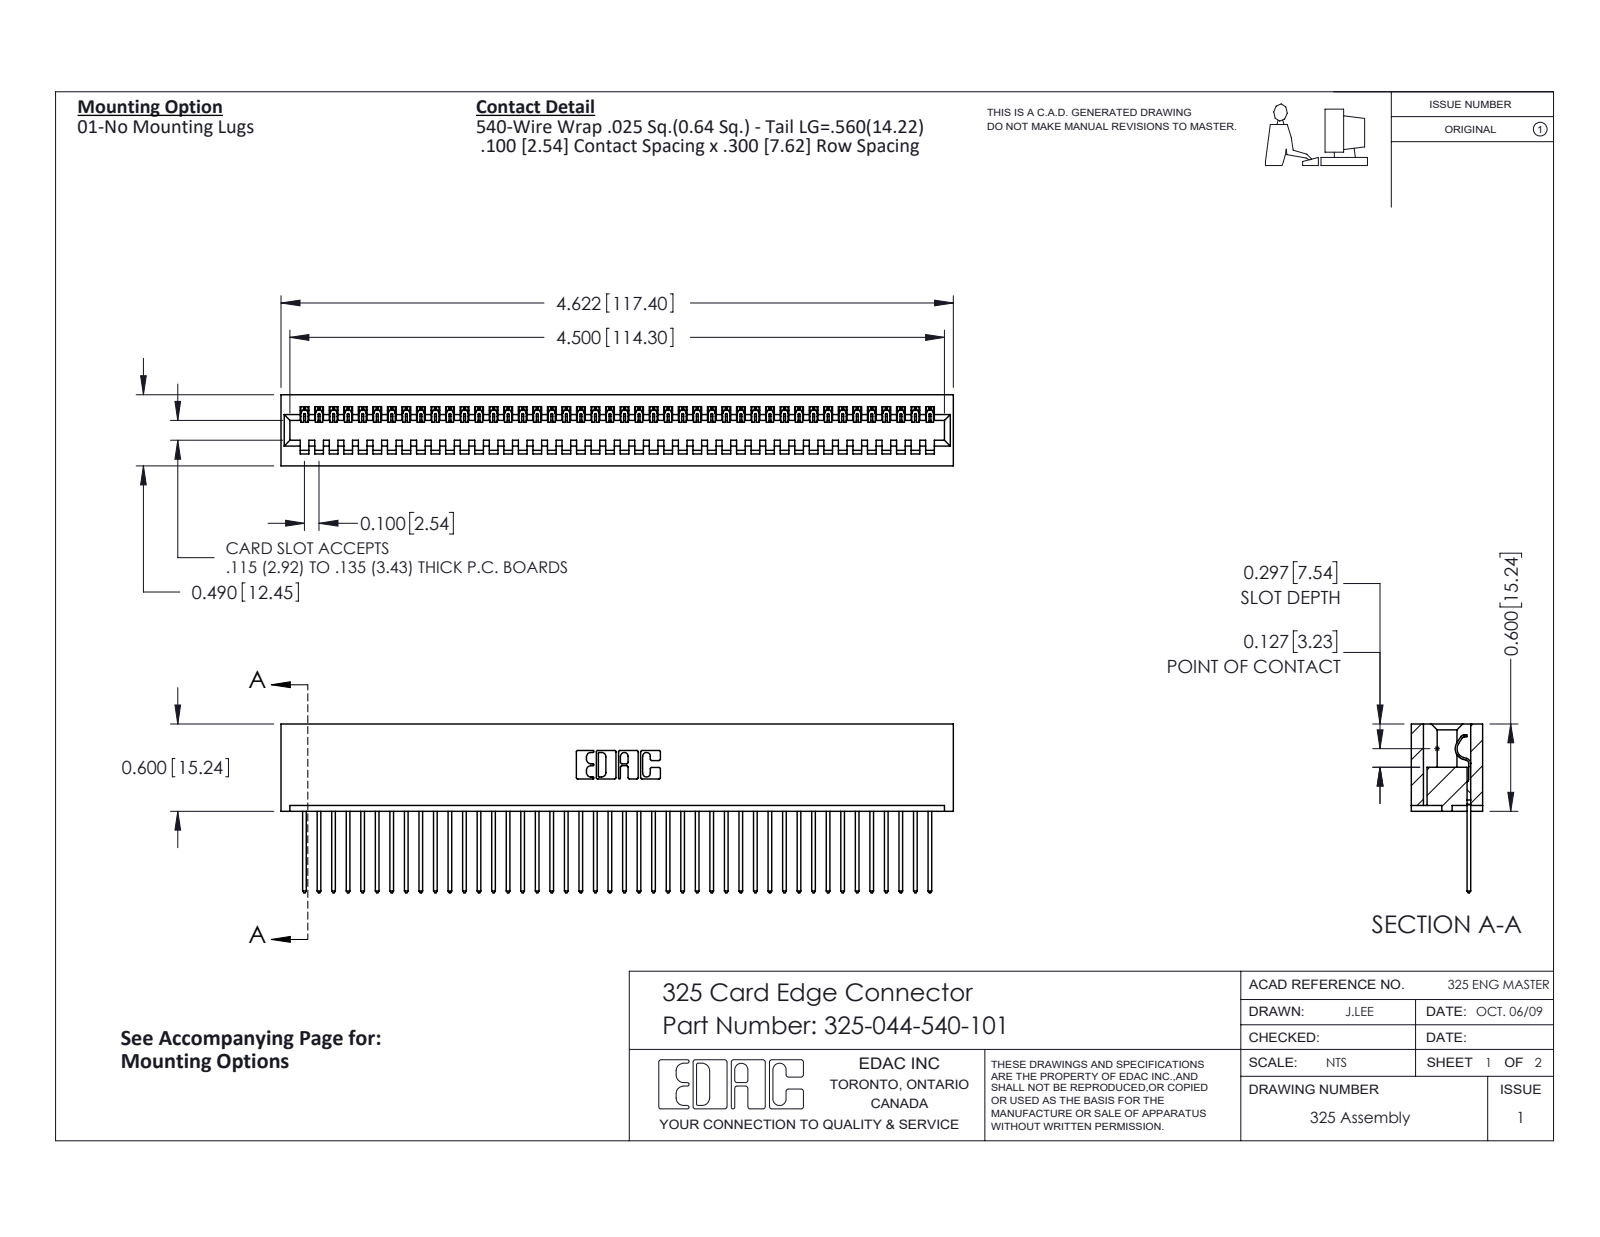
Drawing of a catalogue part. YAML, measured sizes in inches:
part_name: "325 Part_Lugless; 325-044-540-101; 325-292-001_325-293-140"
step_written_by: "SolidWorks 2016 (CONFIG_CONTROL_DESIGN)"
units: inches
bodies: {solids: 45, faces: 2658, planar: 1914, cylindrical: 744, other: 0}
overall_size: [4.622, 1.16, 0.49]
volume: 0.949
surface_area: 27.83
partial_cylinders:
  - {radius: 0.006, count: 88}
  - {radius: 0.01, count: 88}
  - {radius: 0.01, count: 22}
  - {radius: 0.007, count: 6}
  - {radius: 0.031, count: 6}
  - {radius: 0.026, count: 3}
  - {radius: 0.014, count: 1}
  - {radius: 0.022, count: 1}
face_to_face_distances: [0.083, 0.407, 0.49, 0.3, 0.107, 0.383, 0.025, 0.325, 0.56, 0.263]
